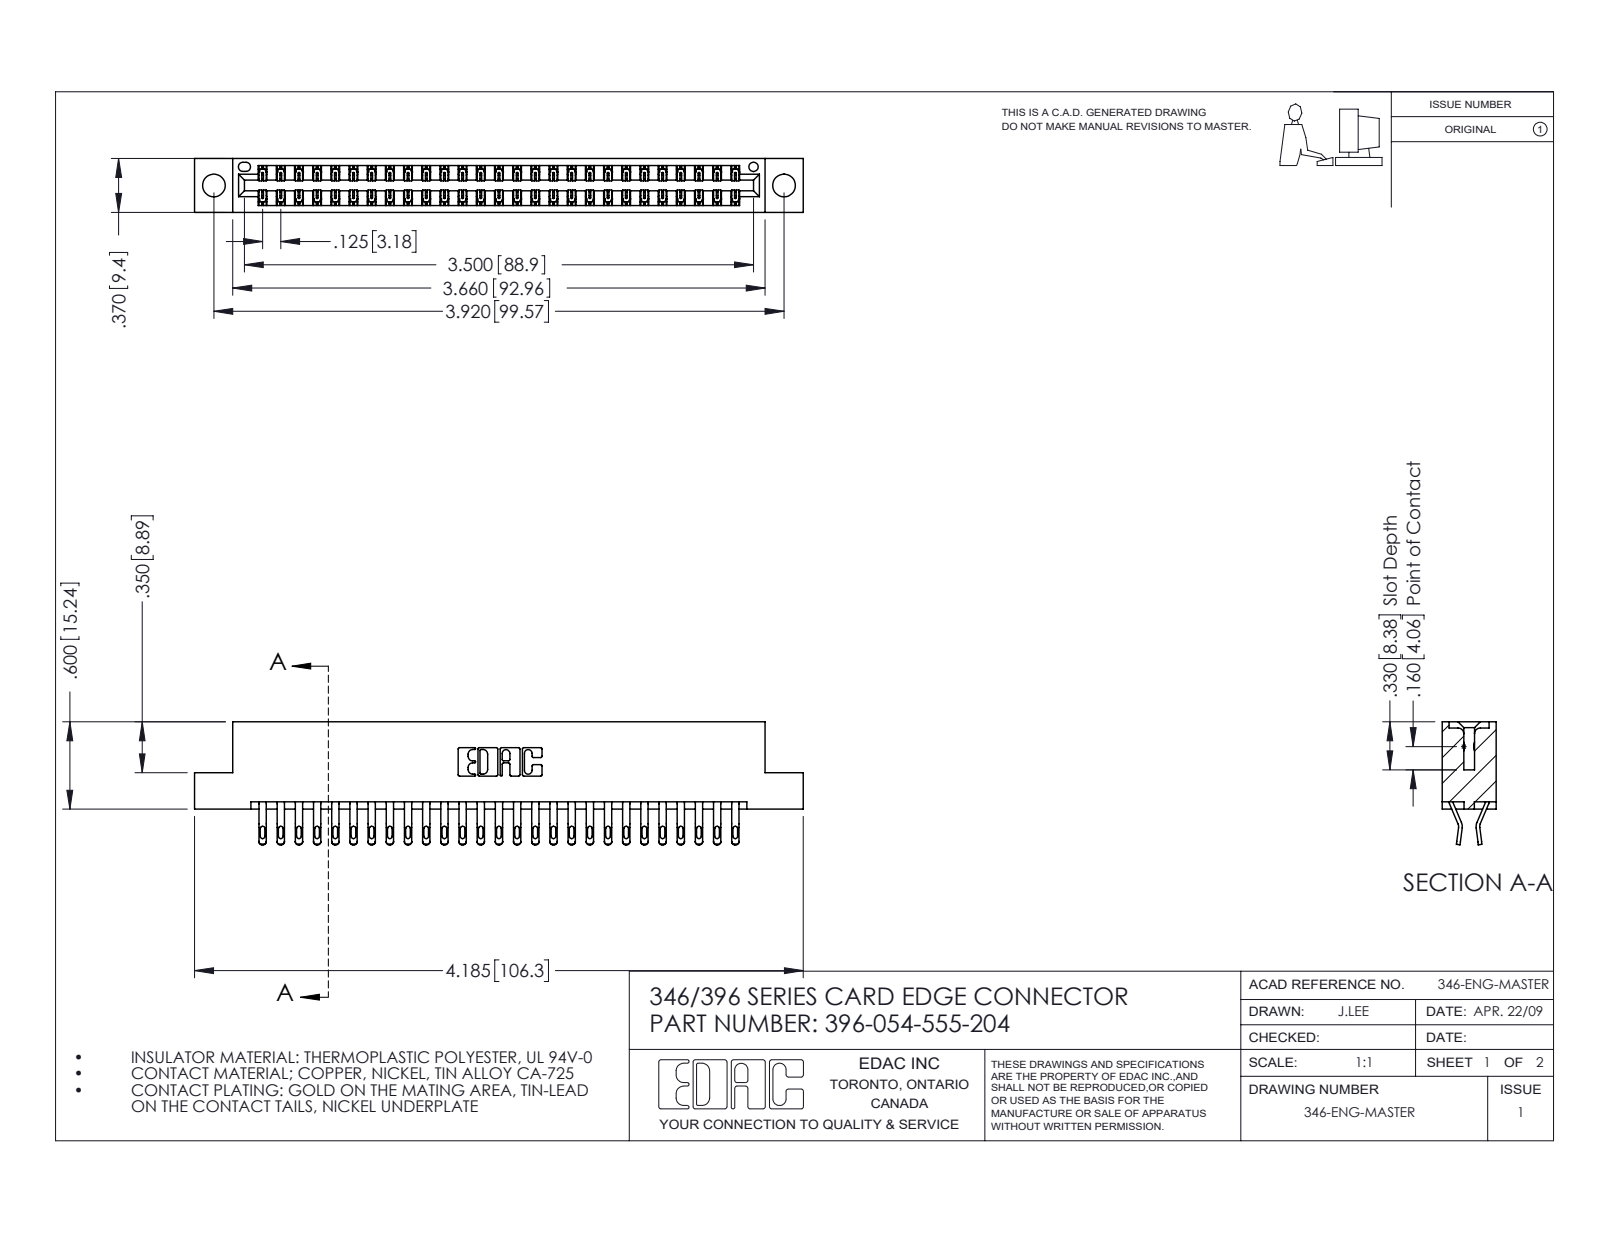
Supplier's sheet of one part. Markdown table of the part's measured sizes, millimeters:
| quantity | value |
| --- | --- |
| part name | 345-292-001_555 Tail; 346 Part_Flush Mounting Lugs - 0.156 Dia-TH; 396-054-555-204 |
| STEP written by | SolidWorks 2016 (CONFIG_CONTROL_DESIGN) |
| units | millimeters |
| bodies | 55 solids, 3254 faces (1858 planar, 1396 cylindrical, 0 other) |
| overall size | 106.3 × 21.5 × 9.4 |
| volume | 10 300 mm³ |
| surface area | 14 320 mm² |
| round holes (diameter × count) | 4 × 2, 1.6 × 1 |
| partial cylindrical surfaces (radius × count) | 0.4 × 108, 0.5 × 108, 0.2 × 81, 0.3 × 22, 0.2 × 6, 0.8 × 6, 0.7 × 3, 0.3 × 2 |
| main face-to-face distances | 1.2, 8.2, 9.4, 6.4, 0.6, 1.8, 7.6, 7, 3.8, 5.6 |
| hole center spacings | 6.2, 94.3, 99.6 |
